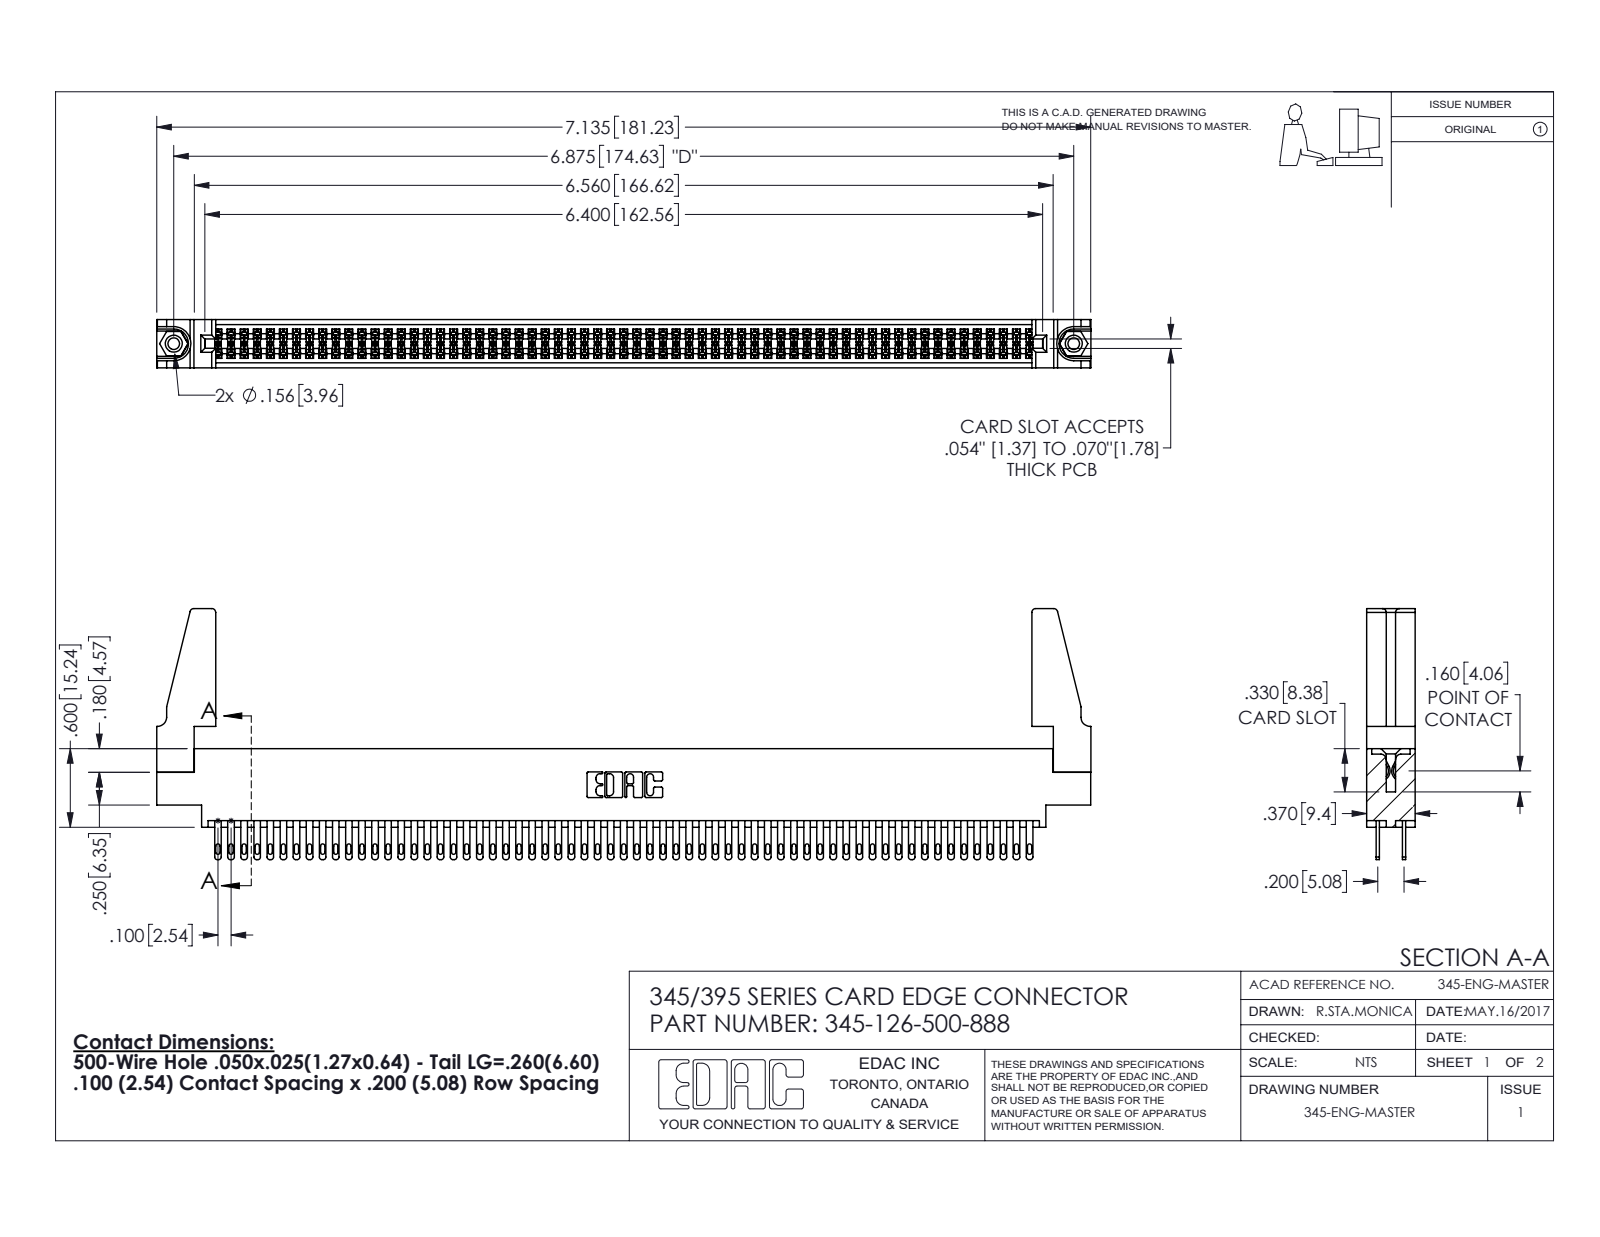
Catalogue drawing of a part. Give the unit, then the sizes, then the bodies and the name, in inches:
Units: inches
Overall size (bounding box): 7.136 × 1.917 × 0.37
Round holes (diameter × count): ⌀0.089 ×2, ⌀0.125 ×2, ⌀0.156 ×2, ⌀0.064 ×1
Round bosses / shafts (diameter × count): ⌀0.155 ×2
Partial cylindrical surfaces — rounded edges, fillets, slot ends (radius × count): R0.006 ×189, R0.016 ×126, R0.02 ×126, R0.01 ×22, R0.03 ×8, R0.007 ×6, R0.031 ×6, R0.026 ×3
Main face-to-face distances: 0.072, 0.298, 0.2, 0.098, 0.272, 0.025, 0.37, 0.225, 0.175, 0.149
Hole centre spacings: 0.27, 6.639, 6.875
Volume: 1.301 in³ · Surface area: 49.09 in²
Bodies: 131 solids, 6050 faces (3558 planar, 2476 cylindrical, 16 other)
Part name (STEP PRODUCT): 345-126-500-888; 345-292-001_345-293-100; 345 Part_0.170 Offset - 0.156 Dia-TH; 345-220-078_345-220-088 (+1 more)
STEP written by: SolidWorks 2016 (CONFIG_CONTROL_DESIGN)
